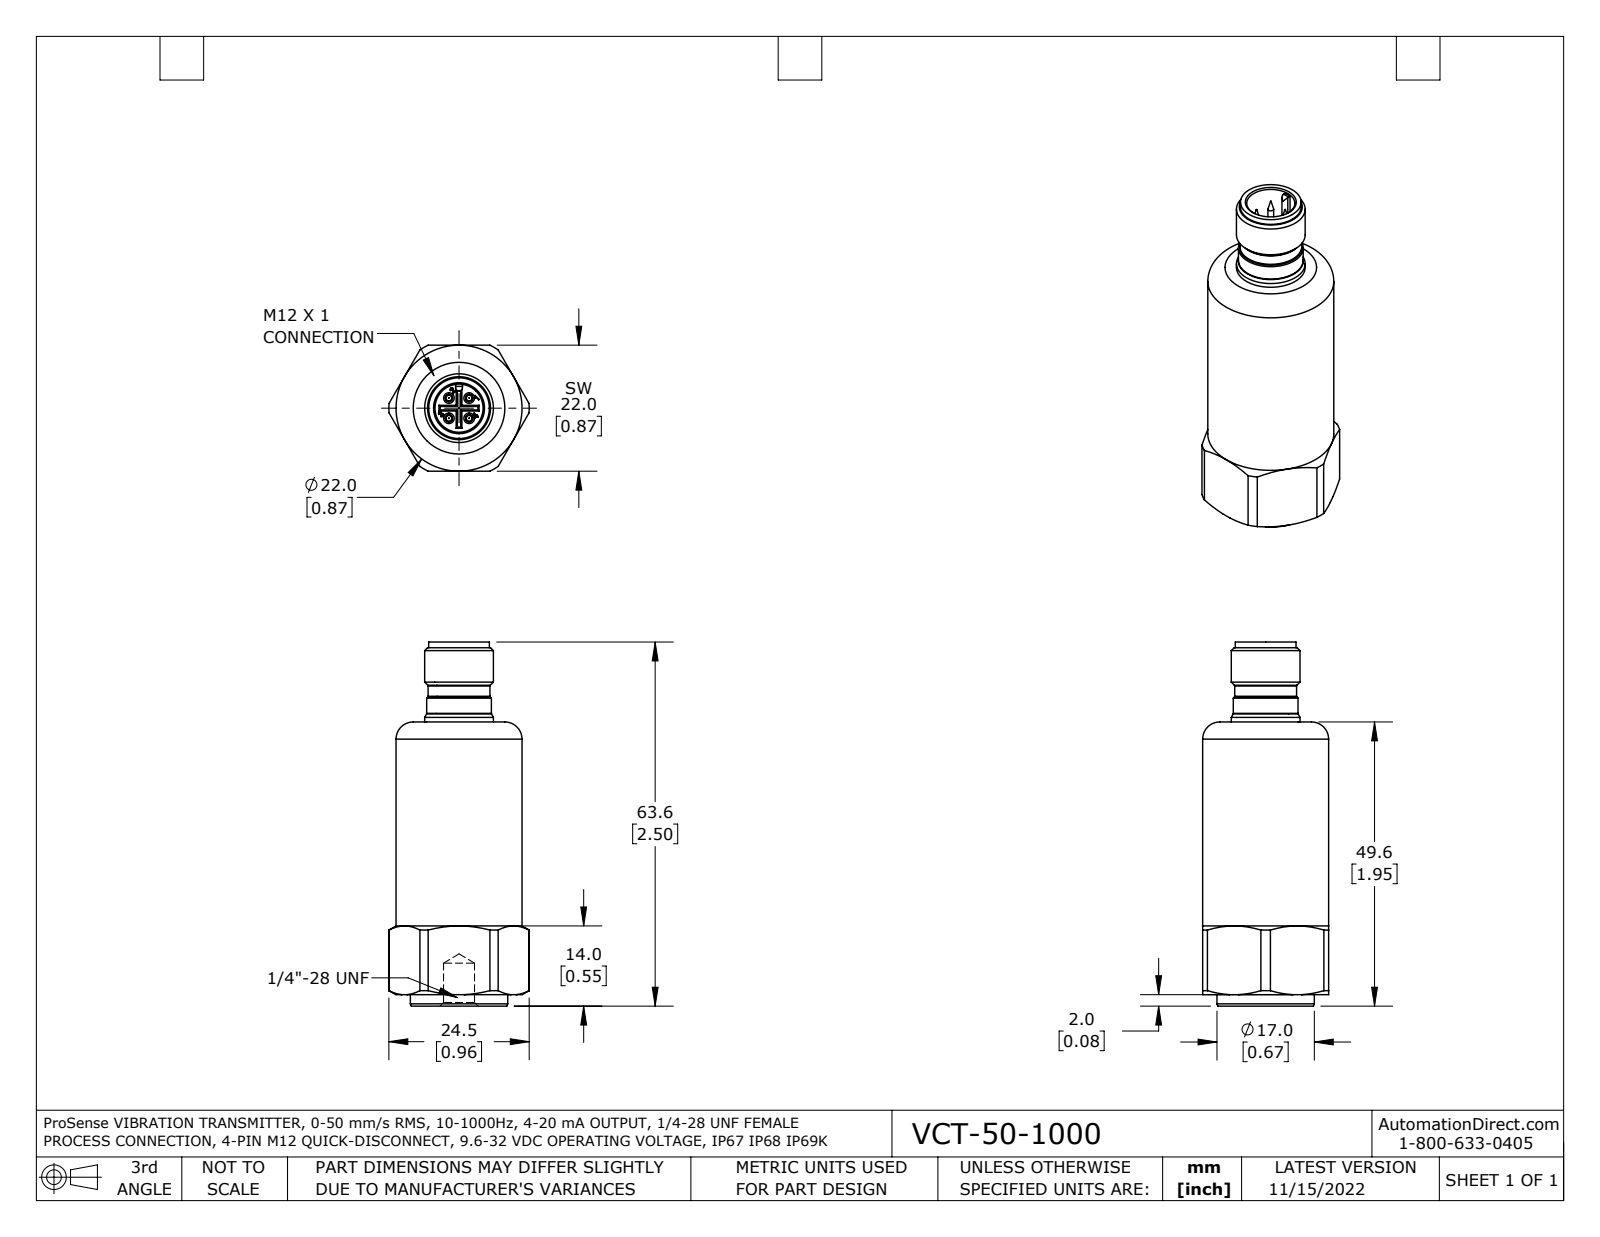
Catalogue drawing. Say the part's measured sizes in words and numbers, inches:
The part is named "VTC001_3D". Its 3-D file was written by "SolidWorks 2021 (AUTOMOTIVE_DESIGN)". It is 1 solid with 218 faces: 62 planar, 61 cylindrical and 95 other. Overall it measures 2.502 by 0.965 by 0.866 inches. Its volume is 1.199 cubic inches and its surface area 8.001 square inches. Round holes: 4 of diameter 0.049, 1 of diameter 0.213, 1 of diameter 0.331. Round bosses or shafts: 4 of diameter 0.047, 4 of diameter 0.039, 1 of diameter 0.866, 1 of diameter 0.669, 1 of diameter 0.472, 1 of diameter 0.445, 1 of diameter 0.425, 1 of diameter 0.417. Partial cylindrical surfaces (rounded edges, fillets, slot ends): 7 of radius 0.008, 1 of radius 0.024, 1 of radius 0.031, 1 of radius 0.482. The main face-to-face distances are 0.866, 0.079, 1.953, 1.874, 2.152, 2.073, 0.199, 0.35, 2.502, 2.423. The hole center spacings are 0.098, 0.139, 0.197.
